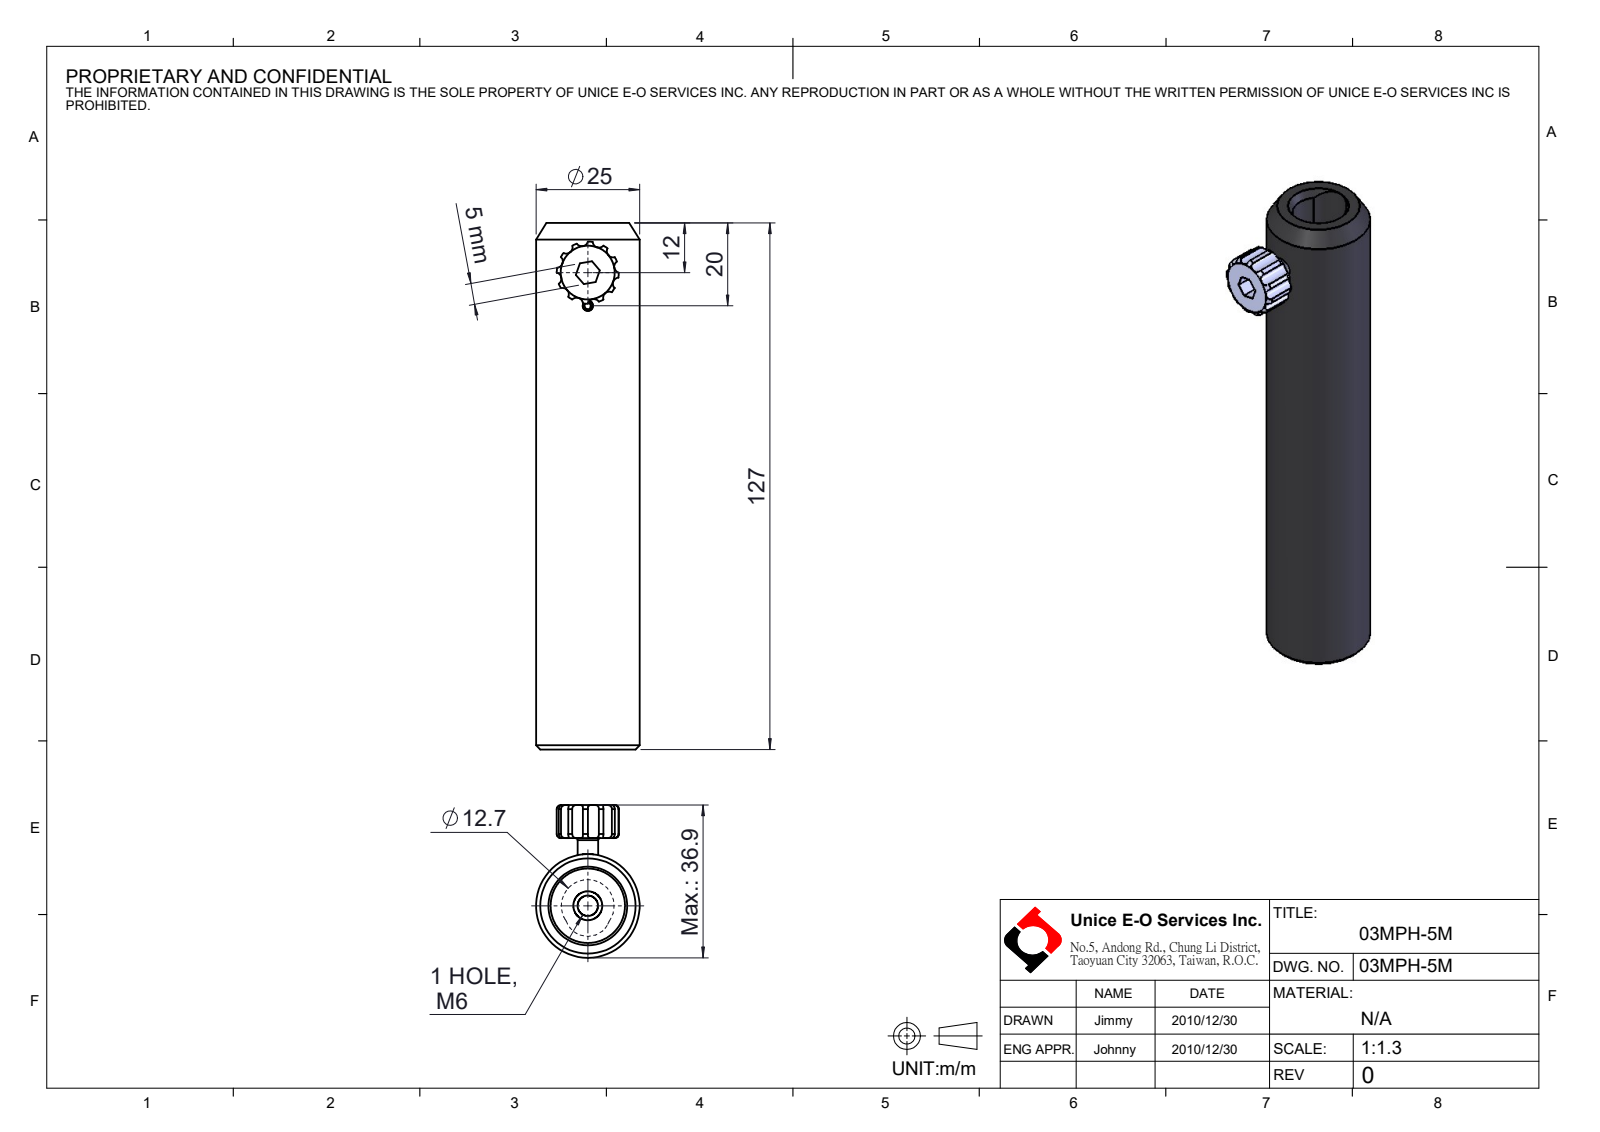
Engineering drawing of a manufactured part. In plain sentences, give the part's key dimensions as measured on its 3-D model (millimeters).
The part is named "03MPH-5M". Its 3-D file was written by "SolidWorks 2016 (CONFIG_CONTROL_DESIGN)". It is 0 solids with 97 faces: 17 planar, 42 cylindrical and 38 other. Overall it measures 127 by 36.85 by 25 millimeters. Round holes: 1 of diameter 2.5, 1 of diameter 5, 1 of diameter 19. Round bosses or shafts: 1 of diameter 25, 1 of diameter 4.94. Partial cylindrical surfaces (rounded edges, fillets, slot ends): 12 of radius 1.5, 1 of radius 5.5, 1 of radius 6.35, 1 of radius 7.5. The main face-to-face distances are 127, 8, 5.1, 4.2, 3.8, 3.85, 8.05, 11.85, 1.5.
